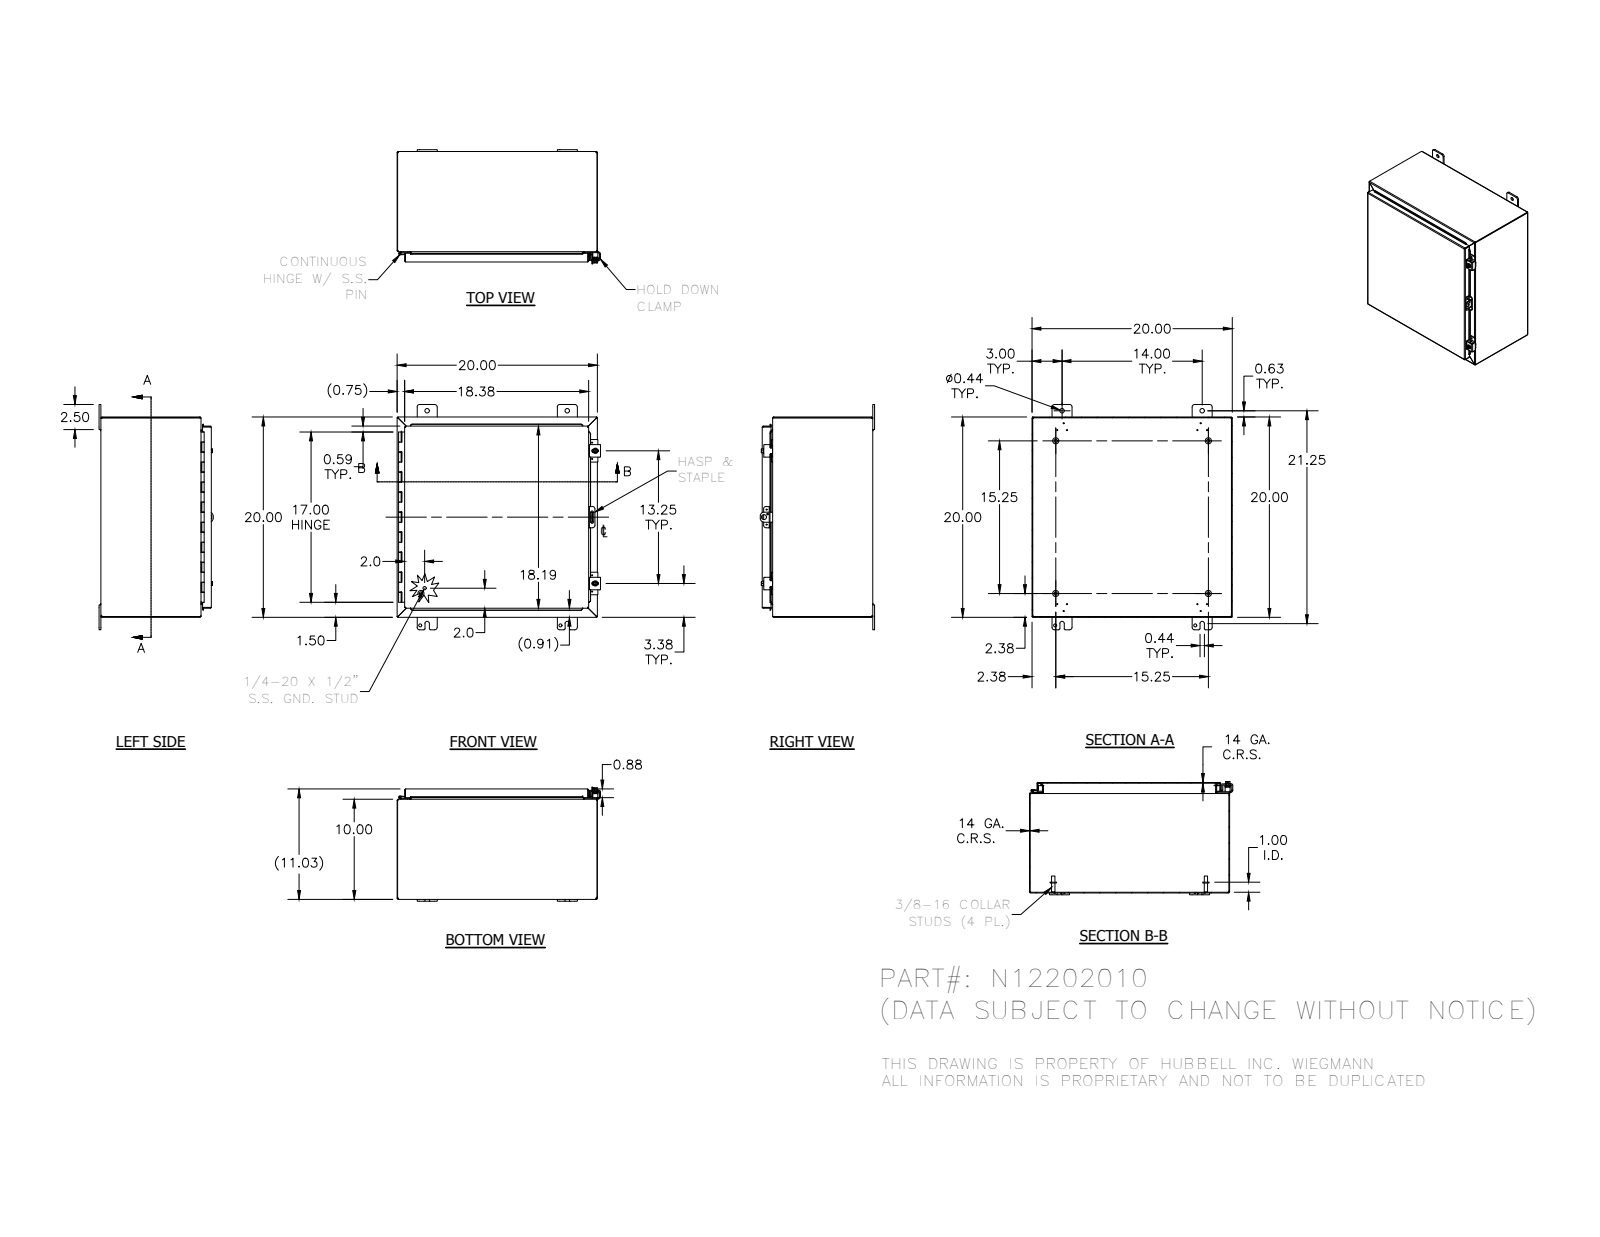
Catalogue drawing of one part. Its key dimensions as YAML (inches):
part_name: "N12202010; 34840; 38420; N12202010BKP (+8 more)"
step_written_by: "Autodesk Inventor 2012 (AUTOMOTIVE_DESIGN)"
units: inches
bodies: {solids: 27, faces: 948, planar: 511, cylindrical: 320, other: 117}
overall_size: [22.5, 20.311, 11.41]
volume: 144.8
surface_area: 3779
round_holes:
  - {diameter: 0.12, count: 12}
  - {diameter: 0.11, count: 7}
  - {diameter: 0.313, count: 4}
  - {diameter: 0.438, count: 4}
  - {diameter: 0.211, count: 2}
  - {diameter: 0.281, count: 2}
  - {diameter: 0.3, count: 2}
  - {diameter: 0.125, count: 1}
  - {diameter: 0.156, count: 1}
  - {diameter: 0.5, count: 1}
round_bosses_or_shafts:
  - {diameter: 0.625, count: 4}
  - {diameter: 0.33, count: 4}
  - {diameter: 0.25, count: 4}
  - {diameter: 0.52, count: 2}
  - {diameter: 0.5, count: 2}
  - {diameter: 0.35, count: 2}
  - {diameter: 0.115, count: 2}
  - {diameter: 0.337, count: 1}
partial_cylinders:
  - {radius: 0.03, count: 27}
  - {radius: 0.063, count: 25}
  - {radius: 0.125, count: 25}
  - {radius: 0.25, count: 25}
  - {radius: 0.031, count: 23}
  - {radius: 0.105, count: 23}
  - {radius: 0.07, count: 8}
  - {radius: 0.1, count: 4}
face_to_face_distances: [0.074, 19.926, 10.959, 20, 19.852, 10.885, 11.033, 9.926, 1.033, 10]
hole_center_spacings: [14, 0.759, 0.839, 0.94, 0.969, 1.593, 1.995, 13.375]
